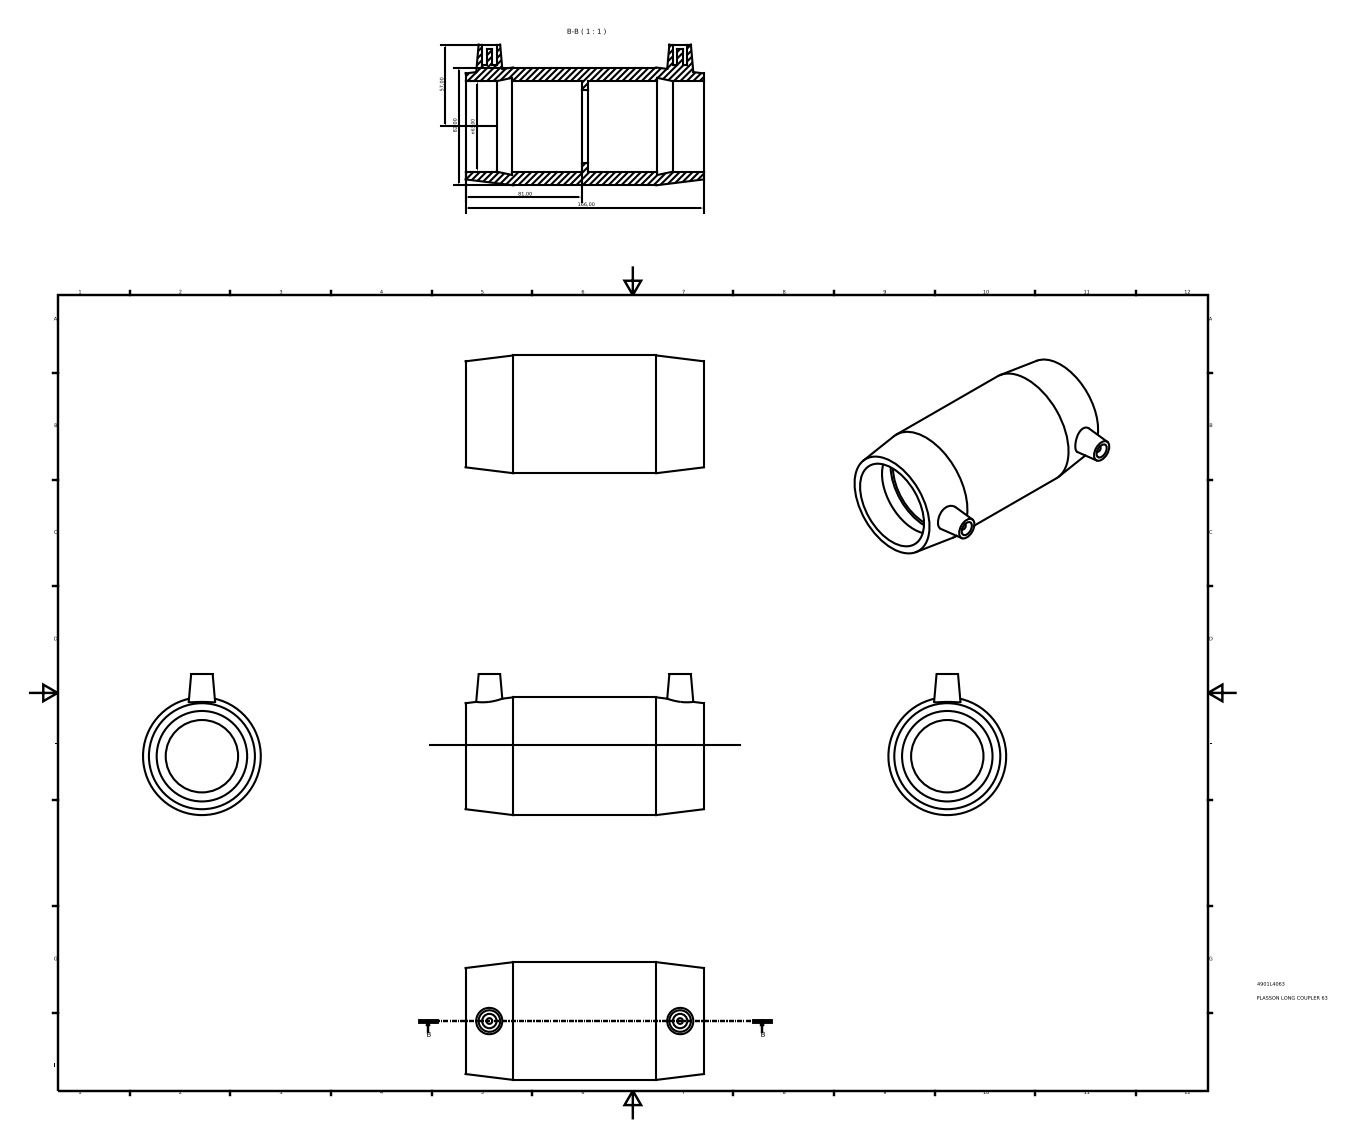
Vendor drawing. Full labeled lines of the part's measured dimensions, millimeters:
Part name (STEP PRODUCT): 4901L4063
STEP written by: Autodesk Inventor 2015 (AUTOMOTIVE_DESIGN)
Units: millimetres
Bodies: 1 solid, 28 faces (12 planar, 10 cylindrical, 6 other)
Overall size (bounding box): 166 × 98 × 82
Volume: 330 791 mm³ · Surface area: 83 419 mm²
Round holes (diameter × count): ⌀10 ×2, ⌀50.4 ×1, ⌀63 ×1
Round bosses / shafts (diameter × count): ⌀4 ×2, ⌀82 ×1
Main face-to-face distances: 81, 85, 166, 4, 32.4, 133.6, 48.6, 52.6, 101.2, 14
Hole centre spacings: 132.8
